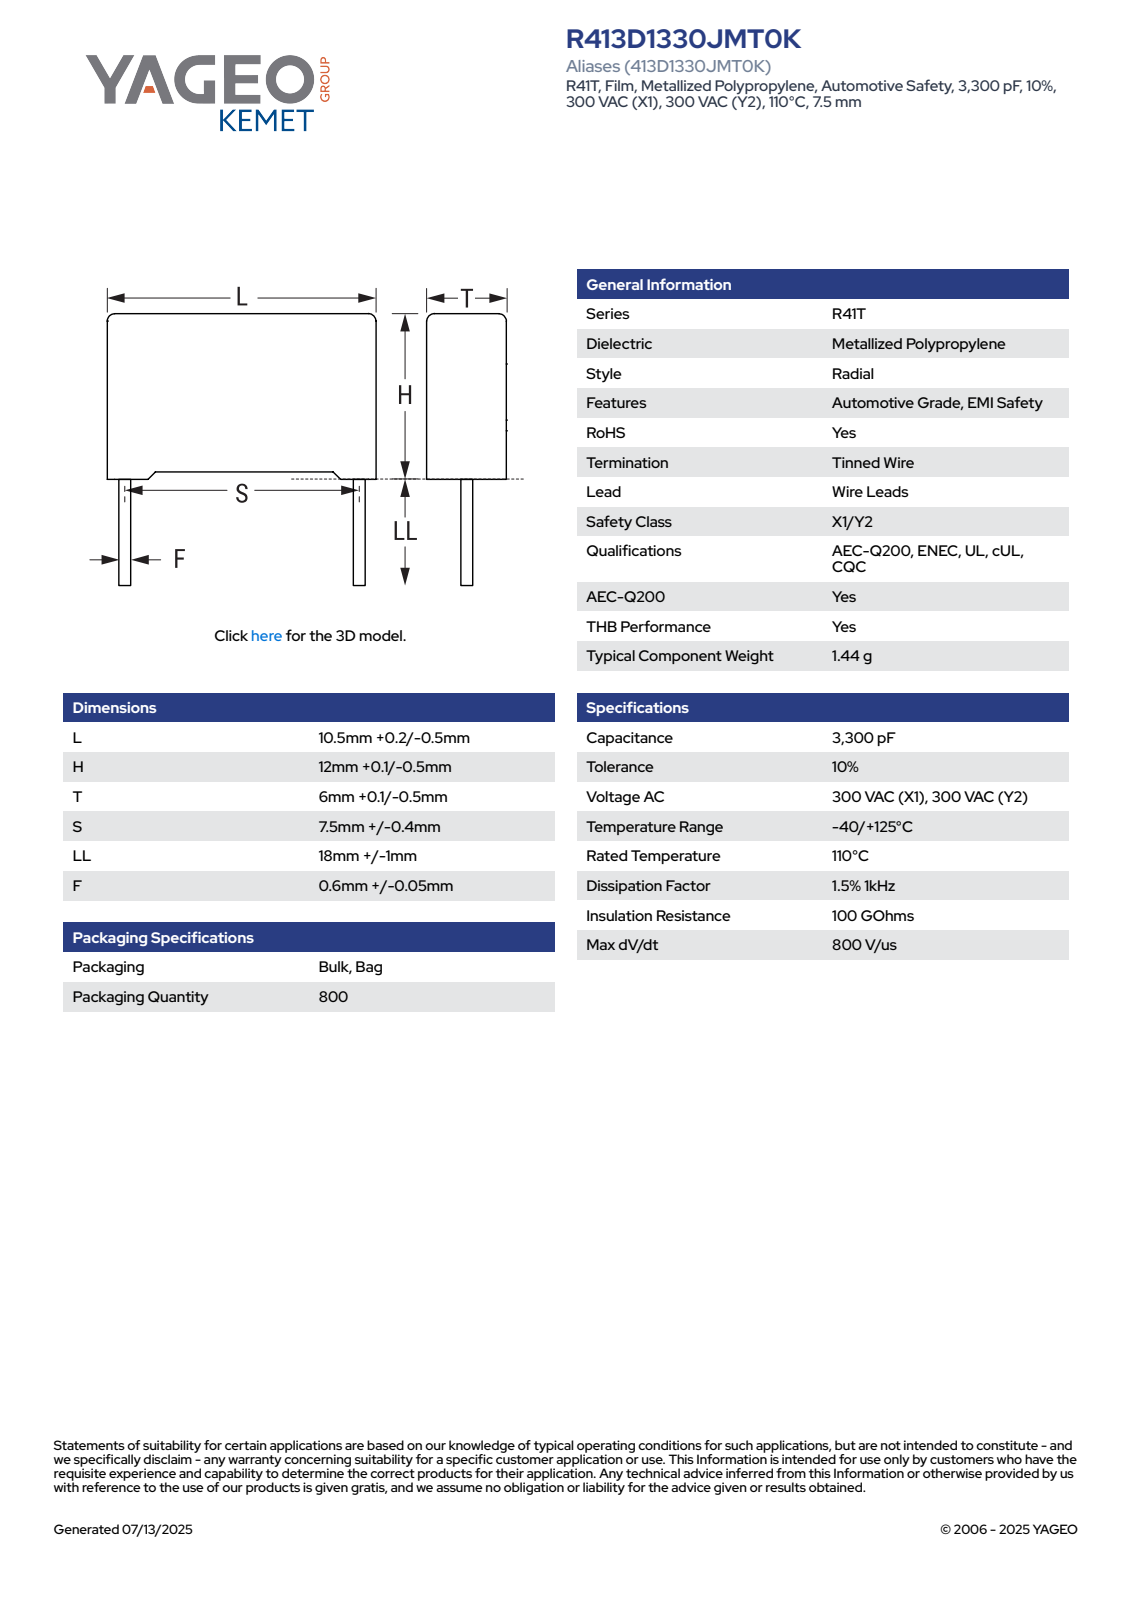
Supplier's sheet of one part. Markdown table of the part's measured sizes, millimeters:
| quantity | value |
| --- | --- |
| part name | CFR_RB2_10.5X12X6_L10.7H12.1T6.1S7.5LL19F0.65 |
| STEP written by | SolidWorks 2021 (AUTOMOTIVE_DESIGN) |
| units | millimeters |
| bodies | 4 solids, 85 faces (77 planar, 8 cylindrical, 0 other) |
| overall size | 31.1 × 10.7 × 6.11 |
| volume | 760 mm³ |
| surface area | 635 mm² |
| round bosses / shafts (diameter × count) | 0.65 × 2 |
| partial cylindrical surfaces (radius × count) | 0.5 × 4 |
| main face-to-face distances | 6.1, 10.7, 11.35, 0.36, 5.74, 0.75, 12.1, 10.34, 5.38, 9.98 |
